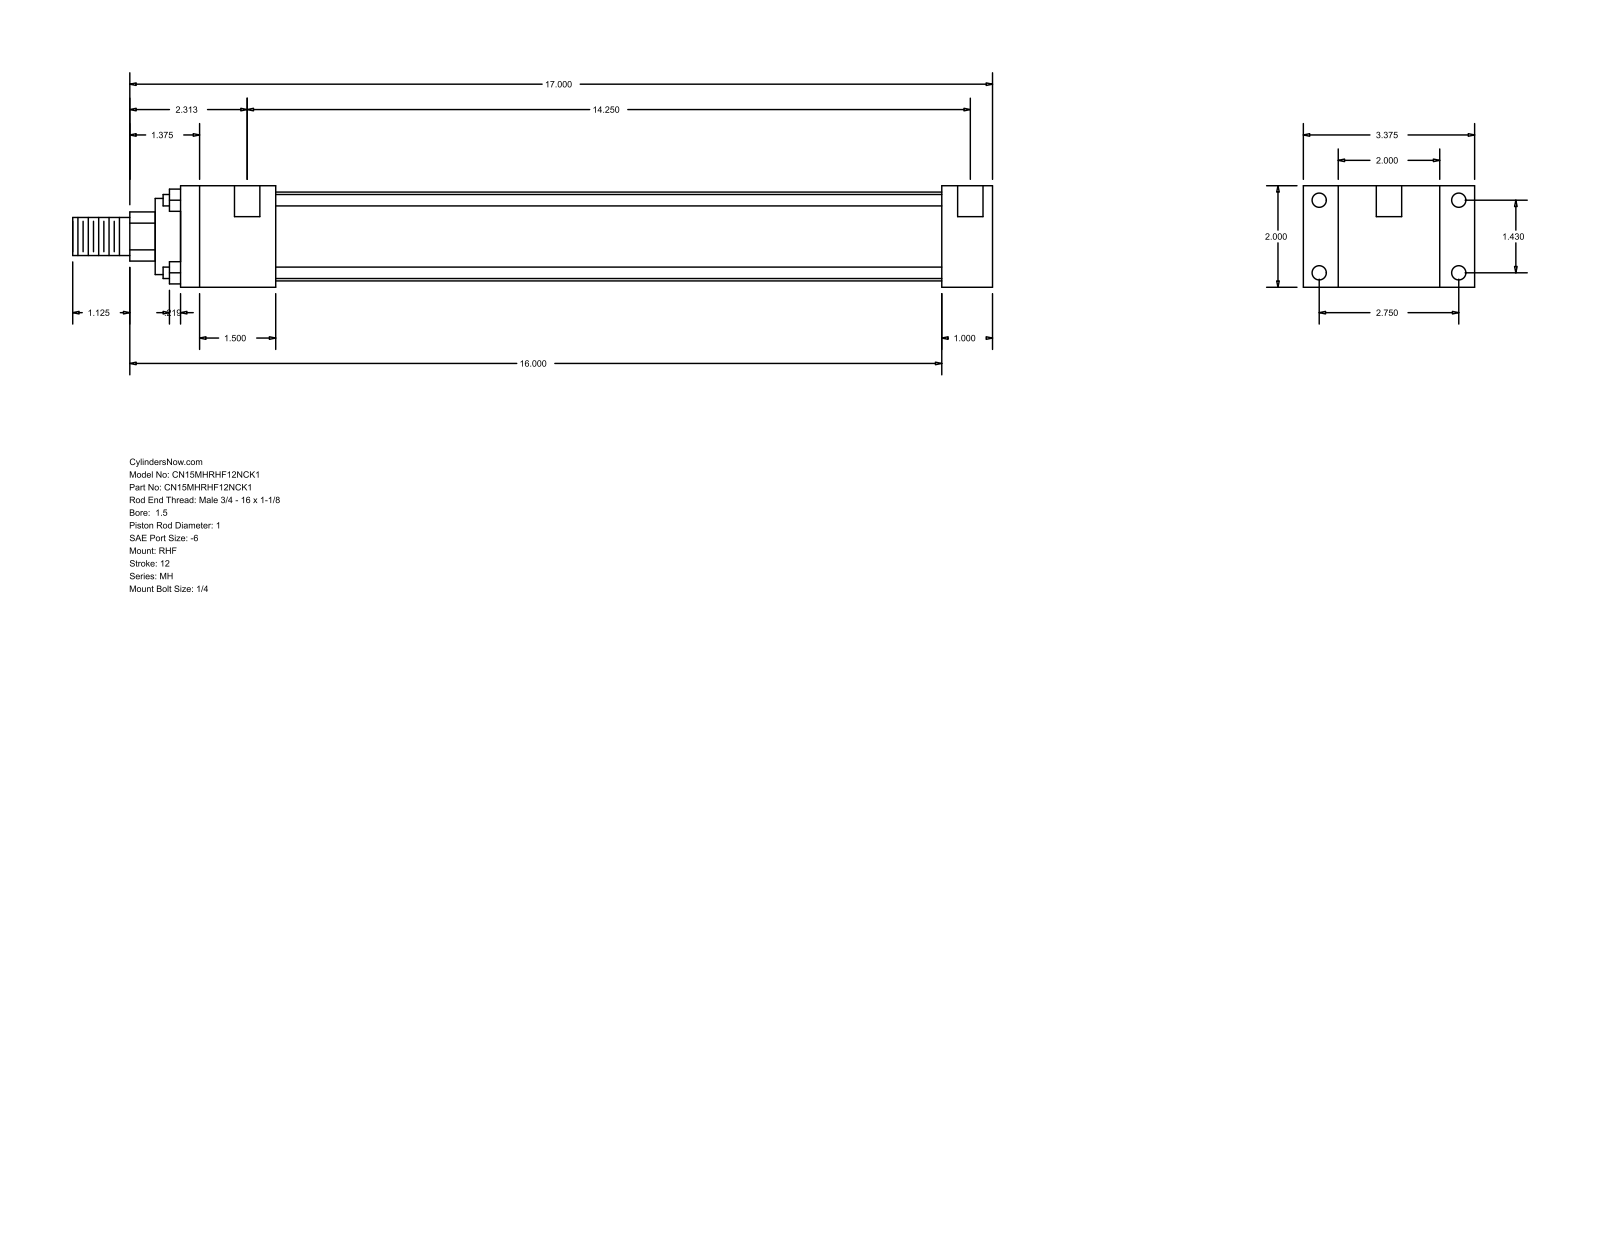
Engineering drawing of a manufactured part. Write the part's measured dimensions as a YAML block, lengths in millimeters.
part_name: "MH_RHF__0150_1"
step_written_by: "GSSL Pune (CONFIG_CONTROL_DESIGN)"
units: millimeters
bodies: {solids: 0, faces: 88, planar: 60, cylindrical: 28, other: 0}
overall_size: [460.38, 85.72, 50.8]
round_holes:
  - {diameter: 5.56, count: 4}
  - {diameter: 7.14, count: 4}
  - {diameter: 12.7, count: 2}
round_bosses_or_shafts:
  - {diameter: 5.71, count: 4}
  - {diameter: 44.45, count: 1}
  - {diameter: 38.1, count: 1}
  - {diameter: 25.4, count: 1}
  - {diameter: 19.05, count: 1}
partial_cylinders:
  - {radius: 12.29, count: 1}
face_to_face_distances: [50.8, 25.4, 17.46, 68.26, 85.72, 406.4, 381, 47.63, 333.37, 358.77]
hole_center_spacings: [36.32, 69.84, 78.72, 365.13, 3.18, 361.95]
